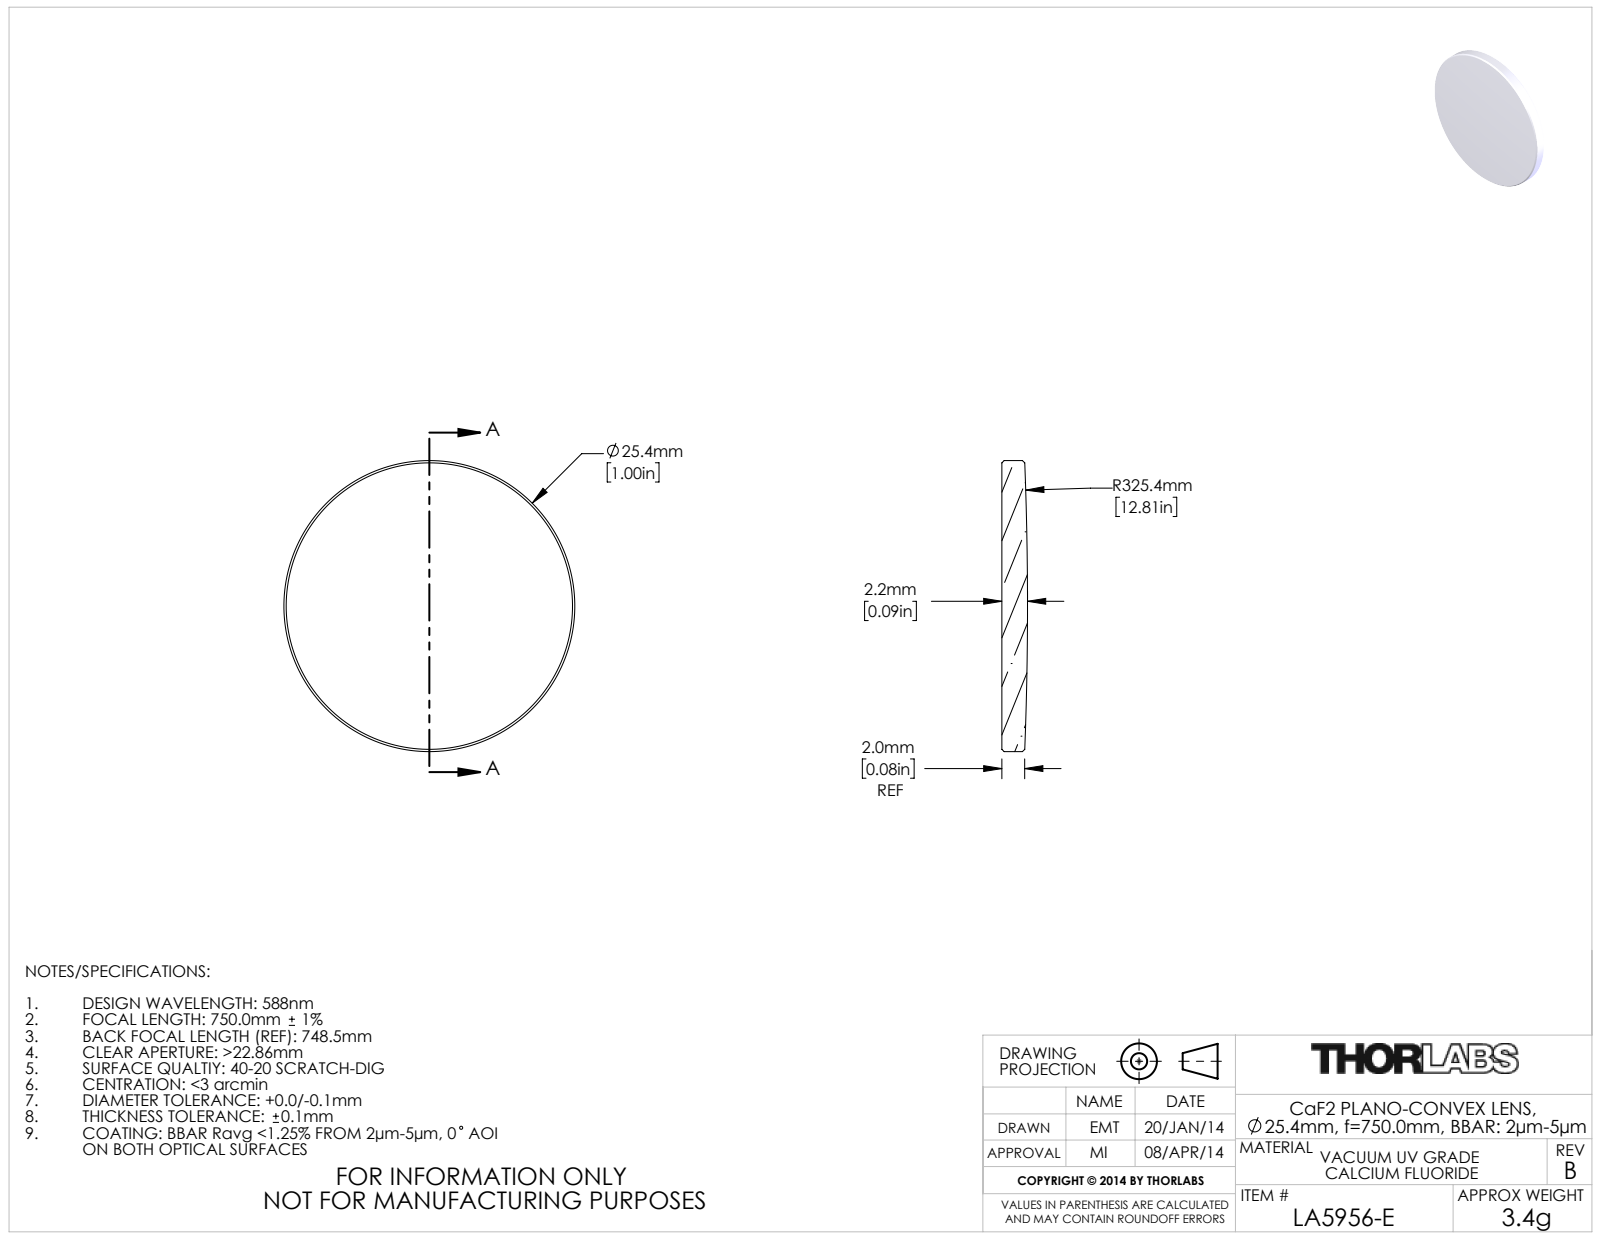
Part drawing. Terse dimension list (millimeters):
name: 20139-E0W
written by: SolidWorks 2018 (CONFIG_CONTROL_DESIGN)
unit: mm
bodies: 1 solid, 9 faces (1 planar, 2 cylindrical, 6 other)
size: 25.4 × 25.4 × 2.24
volume: 1 069 mm³; area: 1 154 mm²
bosses: 1× ⌀25.4
